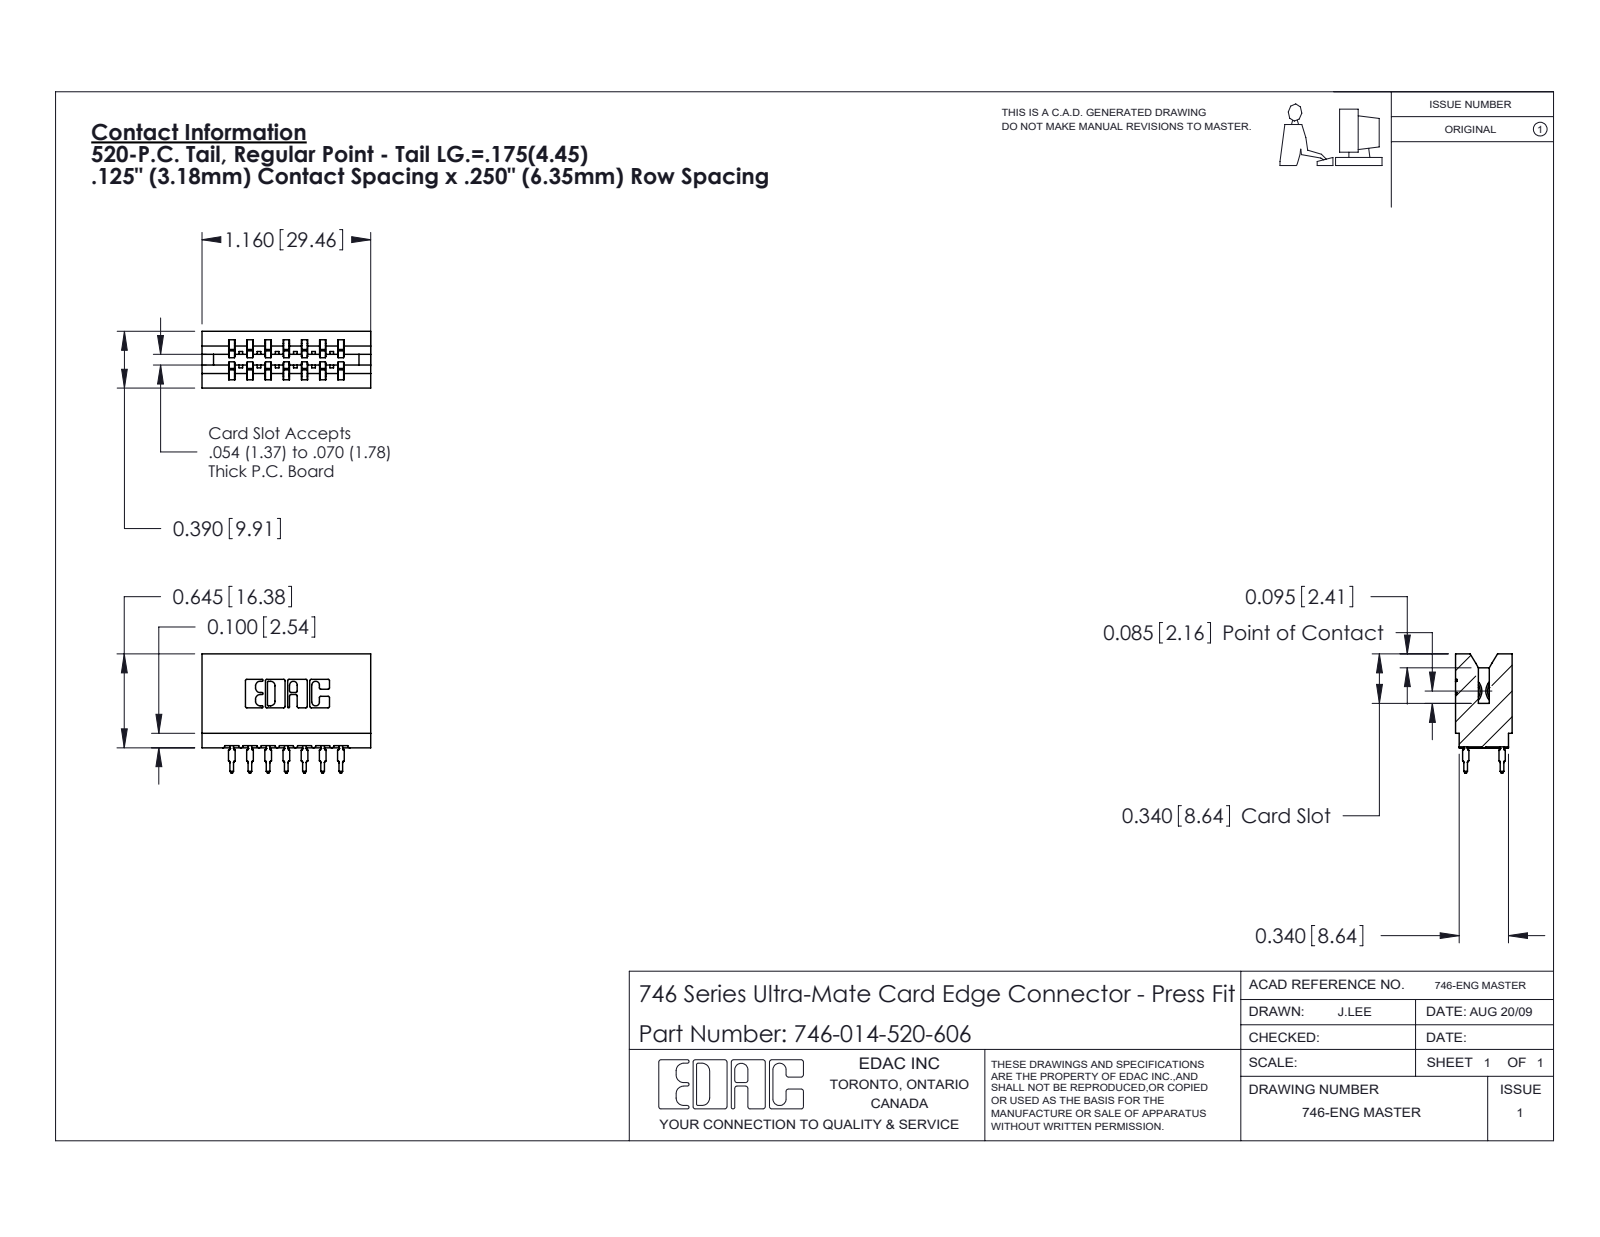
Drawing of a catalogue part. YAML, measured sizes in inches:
part_name: "746 Part_.340 Slot Depth - 06; 746-014-520-606; 746-292-001_520"
step_written_by: "SolidWorks 2020 (CONFIG_CONTROL_DESIGN)"
units: inches
bodies: {solids: 15, faces: 1351, planar: 700, cylindrical: 287, other: 364}
overall_size: [1.16, 0.819, 0.39]
volume: 0.217
surface_area: 6.999
partial_cylinders:
  - {radius: 0.021, count: 28}
  - {radius: 0.01, count: 22}
  - {radius: 0.005, count: 8}
  - {radius: 0.011, count: 8}
  - {radius: 0.015, count: 8}
  - {radius: 0.007, count: 6}
  - {radius: 0.031, count: 6}
  - {radius: 0.026, count: 3}
face_to_face_distances: [0.25, 0.042, 0.333, 0.057, 0.125, 0.5, 0.125, 0.292, 0.208, 0.39]
